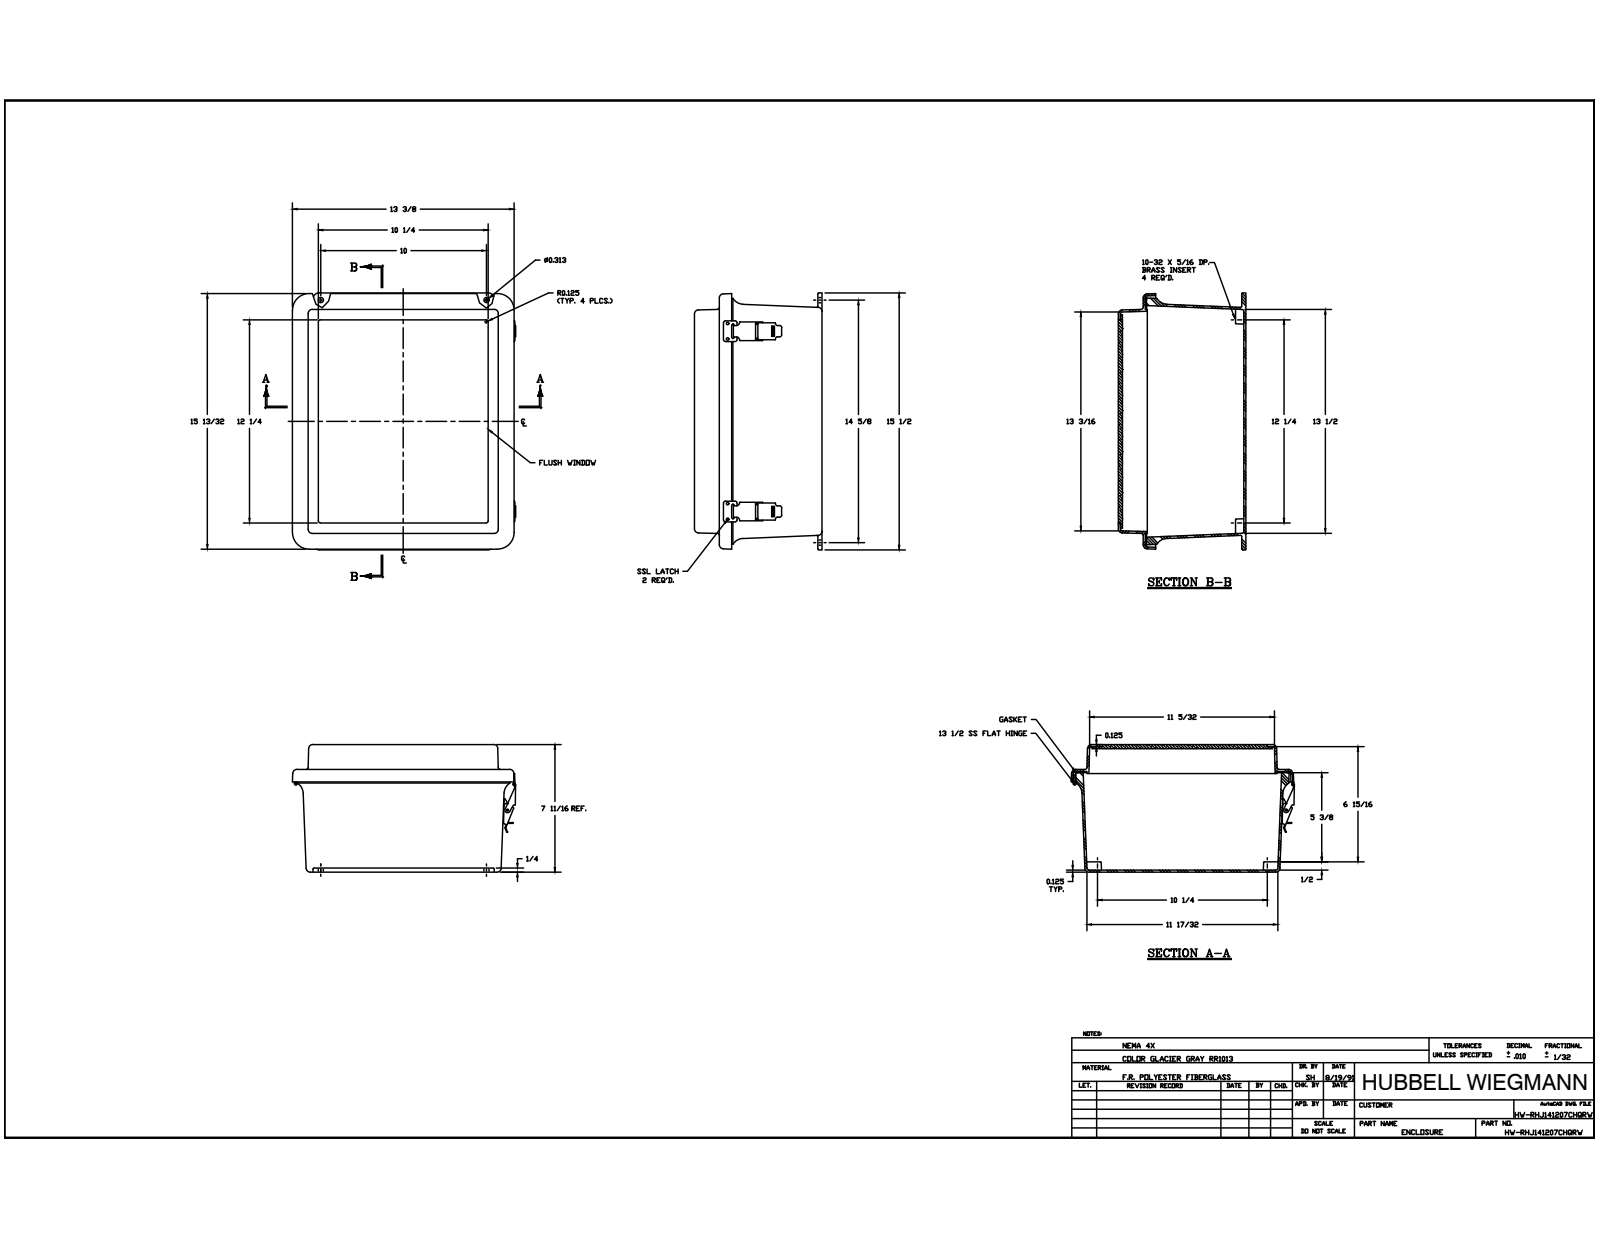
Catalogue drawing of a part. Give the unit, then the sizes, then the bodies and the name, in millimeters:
Units: millimetres
Overall size (bounding box): 393.7 × 343.46 × 195.65
Round holes (diameter × count): ⌀3.56 ×22, ⌀3.33 ×10, ⌀2.64 ×8, ⌀3.86 ×8, ⌀3.3 ×4, ⌀3.96 ×4, ⌀5.54 ×4, ⌀3.43 ×2, ⌀9.52 ×2, ⌀2.16 ×1
Round bosses / shafts (diameter × count): ⌀3.17 ×18, ⌀6.35 ×10, ⌀6.86 ×4, ⌀7.62 ×1, ⌀4.31 ×1, ⌀3.94 ×1, ⌀3.05 ×1
Partial cylindrical surfaces — rounded edges, fillets, slot ends (radius × count): R3.17 ×32, R6.35 ×24, R0.38 ×20, R0.79 ×20, R1.14 ×16, R0.76 ×12, R0.57 ×9, R1.52 ×6
Main face-to-face distances: 3.18, 189.3, 3.17, 6.35, 195.65, 192.47, 186.12, 151.2, 38.1, 154.38
Hole centre spacings: 82.55, 165.1, 276.4, 6.35, 247.65, 276.39, 277.06, 76.2
Volume: 2 245 000 mm³ · Surface area: 1 154 000 mm²
Bodies: 41 solids, 1140 faces (495 planar, 472 cylindrical, 173 other)
Part name (STEP PRODUCT): J1412HL_8; RMINS45821P_315; RMINS45821P_316; RMINS45821P_317 (+8 more)
STEP written by: Autodesk Inventor 2014 (AUTOMOTIVE_DESIGN)
